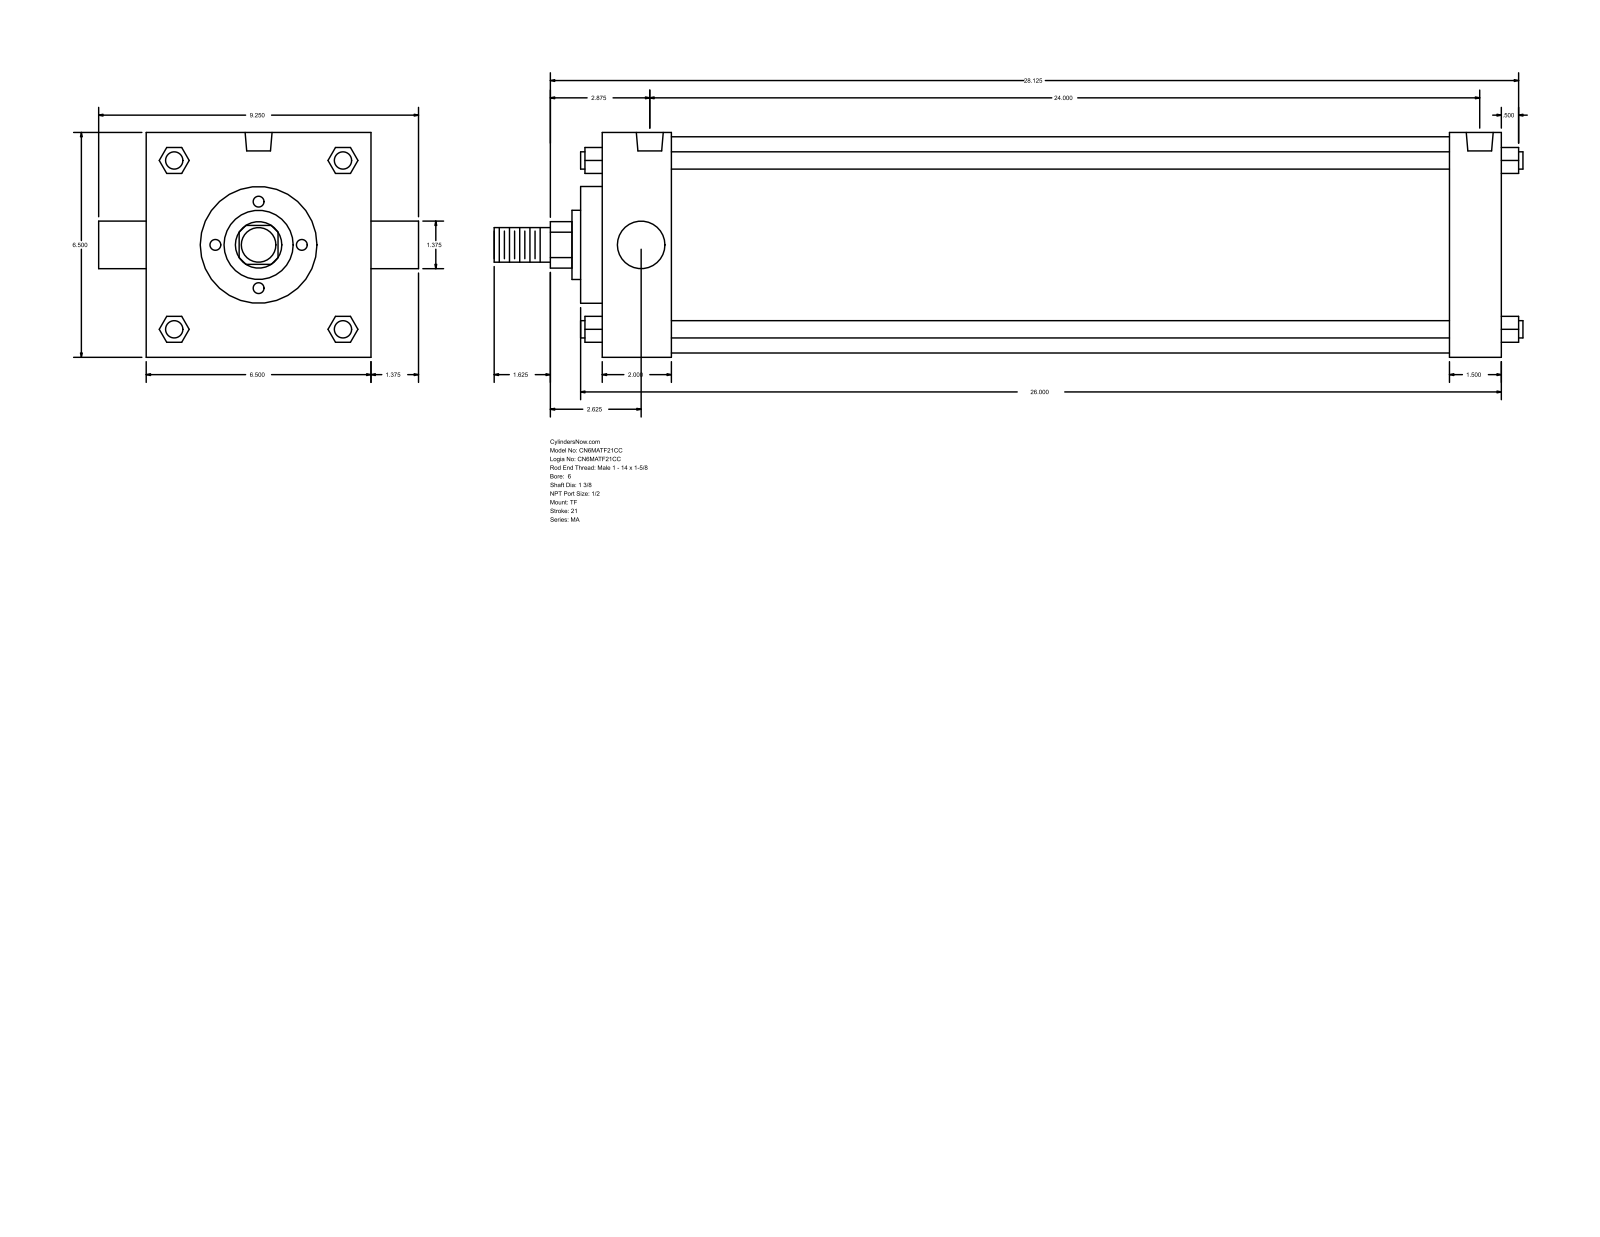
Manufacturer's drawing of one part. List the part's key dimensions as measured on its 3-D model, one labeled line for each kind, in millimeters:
Part name (STEP PRODUCT): MA_TF__0600_1.375
STEP written by: GSSL Pune (CONFIG_CONTROL_DESIGN)
Units: millimetres
Bodies: 0 solids, 122 faces (93 planar, 29 cylindrical, 0 other)
Overall size (bounding box): 755.65 × 234.95 × 165.1
Round holes (diameter × count): ⌀17.46 ×3, ⌀19.77 ×2
Round bosses / shafts (diameter × count): ⌀12.7 ×4, ⌀34.92 ×2, ⌀158.75 ×1, ⌀85.72 ×1, ⌀50.8 ×1, ⌀25.4 ×1
Partial cylindrical surfaces — rounded edges, fillets, slot ends (radius × count): R17.06 ×1
Main face-to-face distances: 165.1, 663.57, 50.8, 625.48, 612.77, 574.68, 38.09, 66.67, 15.87, 641.35
Hole centre spacings: 3.18, 609.59, 612.77
